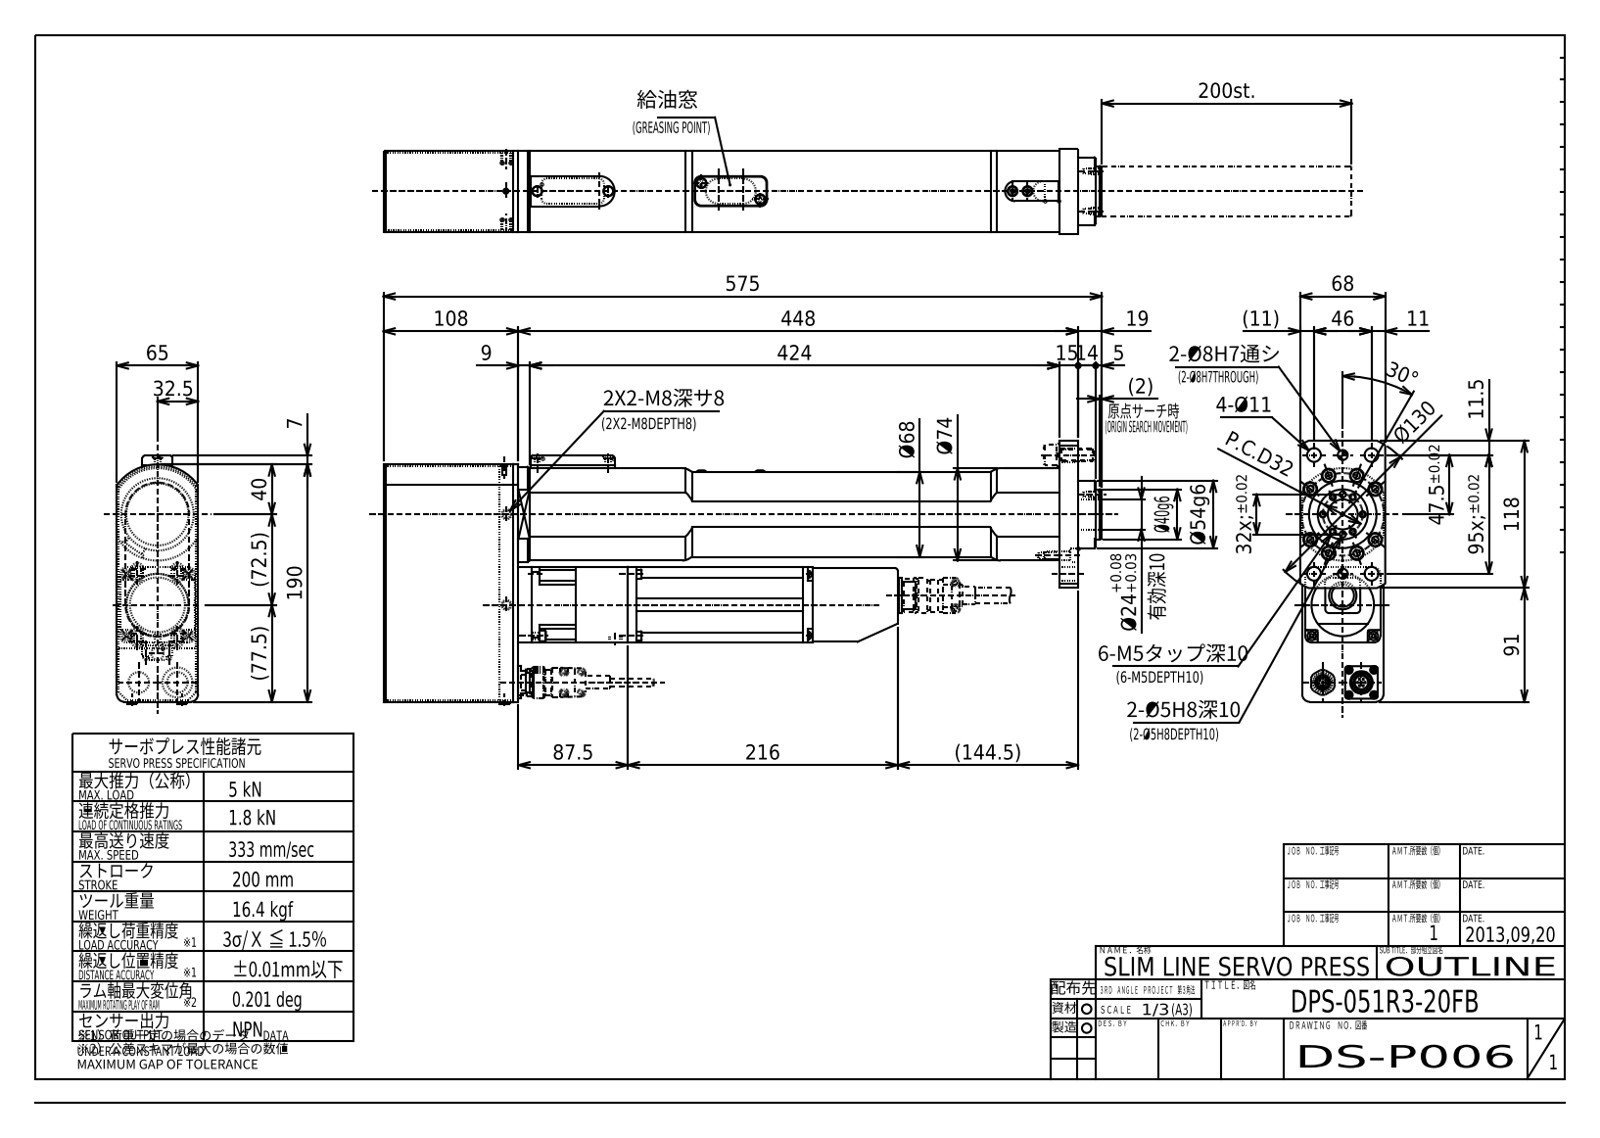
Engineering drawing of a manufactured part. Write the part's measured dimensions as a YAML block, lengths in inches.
part_name: "DPS-051R3-20FB_kp_Shrinkwrap_1; 745_OUTLINE; DPS-051R3-20FB_OUTLINE"
step_written_by: "Autodesk Inventor 2015 (AUTOMOTIVE_DESIGN)"
units: inches
bodies: {solids: 3, faces: 787, planar: 363, cylindrical: 253, other: 171}
overall_size: [22.638, 8.228, 2.677]
volume: 241.1
surface_area: 576.5
round_holes:
  - {diameter: 0.177, count: 10}
  - {diameter: 0.128, count: 7}
  - {diameter: 0.163, count: 6}
  - {diameter: 0.315, count: 6}
  - {diameter: 0.433, count: 5}
  - {diameter: 0.13, count: 4}
  - {diameter: 0.197, count: 4}
  - {diameter: 0.217, count: 4}
  - {diameter: 0.097, count: 2}
  - {diameter: 0.335, count: 2}
  - {diameter: 0.157, count: 1}
  - {diameter: 0.343, count: 1}
round_bosses_or_shafts:
  - {diameter: 2.677, count: 1}
  - {diameter: 2.323, count: 1}
  - {diameter: 2.126, count: 1}
  - {diameter: 1.004, count: 1}
  - {diameter: 0.925, count: 1}
  - {diameter: 0.866, count: 1}
  - {diameter: 0.863, count: 1}
  - {diameter: 0.815, count: 1}
partial_cylinders:
  - {radius: 0.079, count: 31}
  - {radius: 0.197, count: 16}
  - {radius: 0.02, count: 8}
  - {radius: 0.098, count: 4}
  - {radius: 0.394, count: 3}
  - {radius: 0.118, count: 2}
  - {radius: 0.177, count: 2}
  - {radius: 0.236, count: 2}
face_to_face_distances: [2.559, 0.098, 2.362, 2.461, 0.591, 0.433, 4.232, 1.87, 1.929, 21.89]
hole_center_spacings: [0.63, 0.326, 0.891, 0.906, 1.091, 1.217, 1.361, 1.45]
